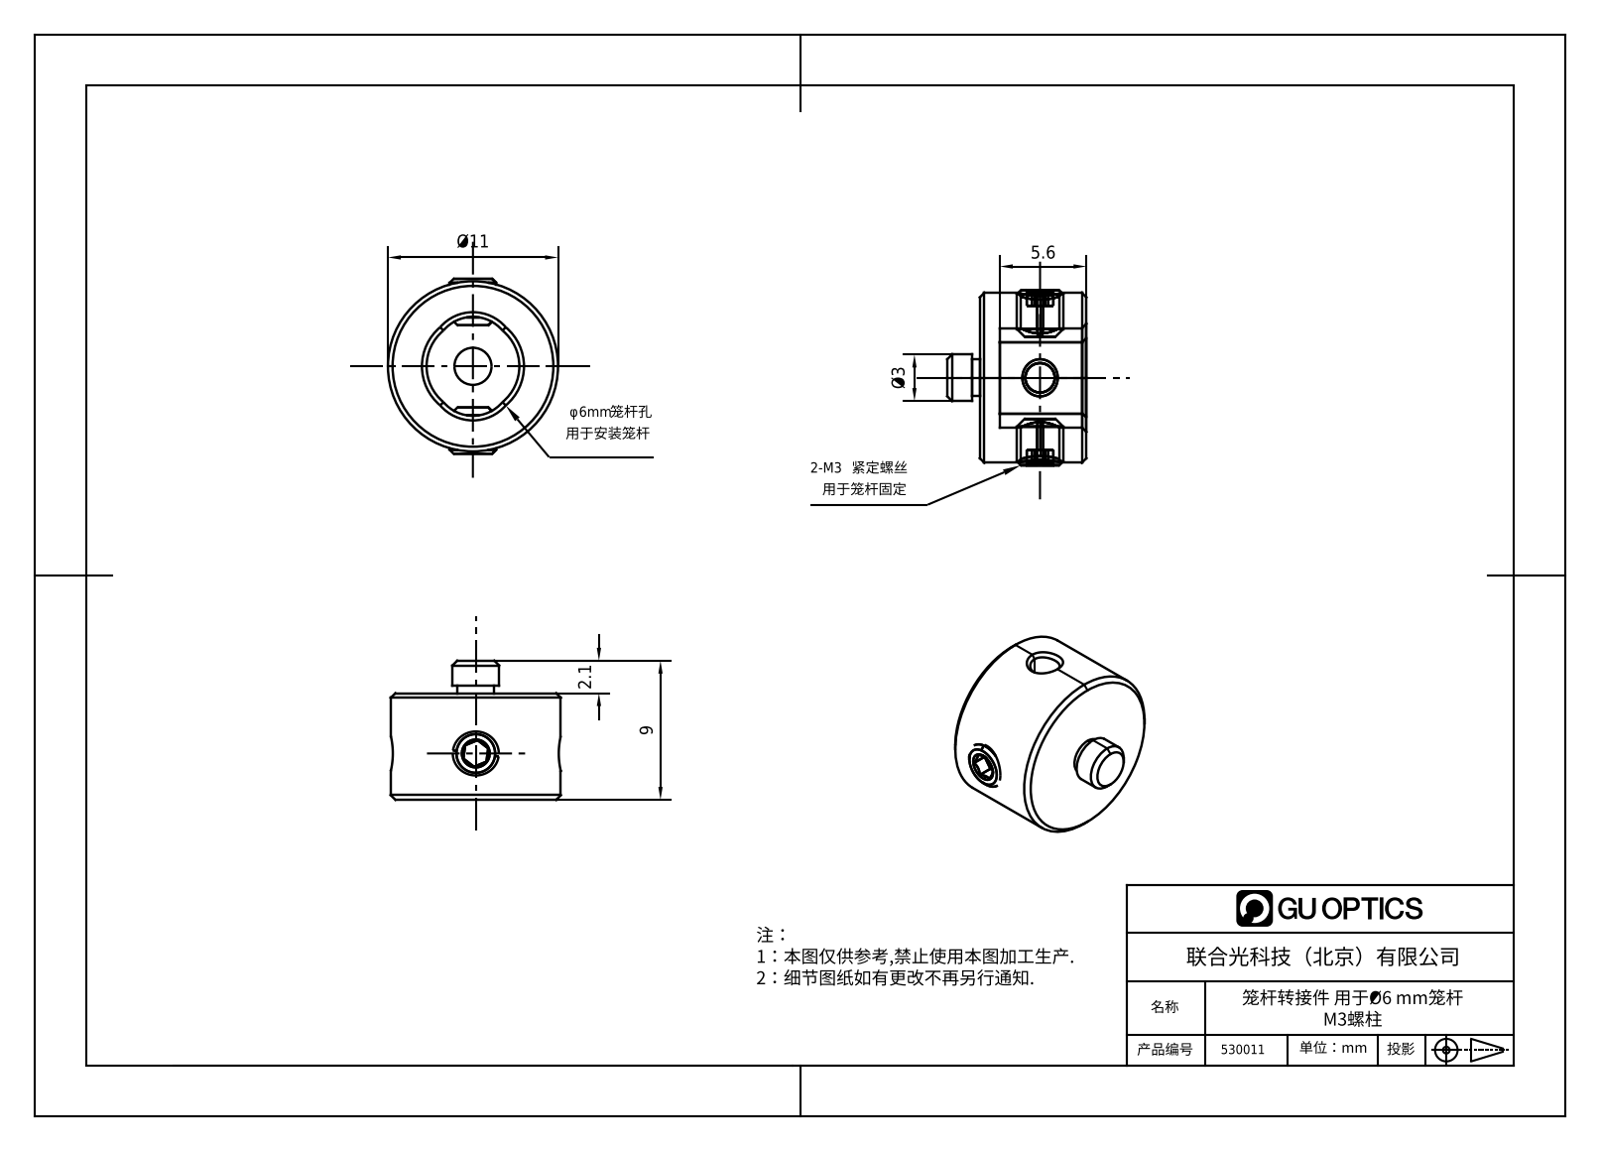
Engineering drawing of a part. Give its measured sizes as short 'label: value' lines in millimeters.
name: 2.4.2.5_LZZ-C6M_M3转6mm通孔
written by: SolidWorks 2018 (AUTOMOTIVE_DESIGN)
unit: mm
bodies: 0 solids, 75 faces (21 planar, 23 cylindrical, 31 other)
size: 11.31 × 11 × 9
holes: 1× ⌀1.9, 1× ⌀2.5
bosses: 2× ⌀3, 1× ⌀11, 1× ⌀2.4
rounds: 2× R2.5, 1× R3
face distances: 6.9, 3, 8.32, 1.5, 9, 2.1, 1, 10.32, 2, 7.32
